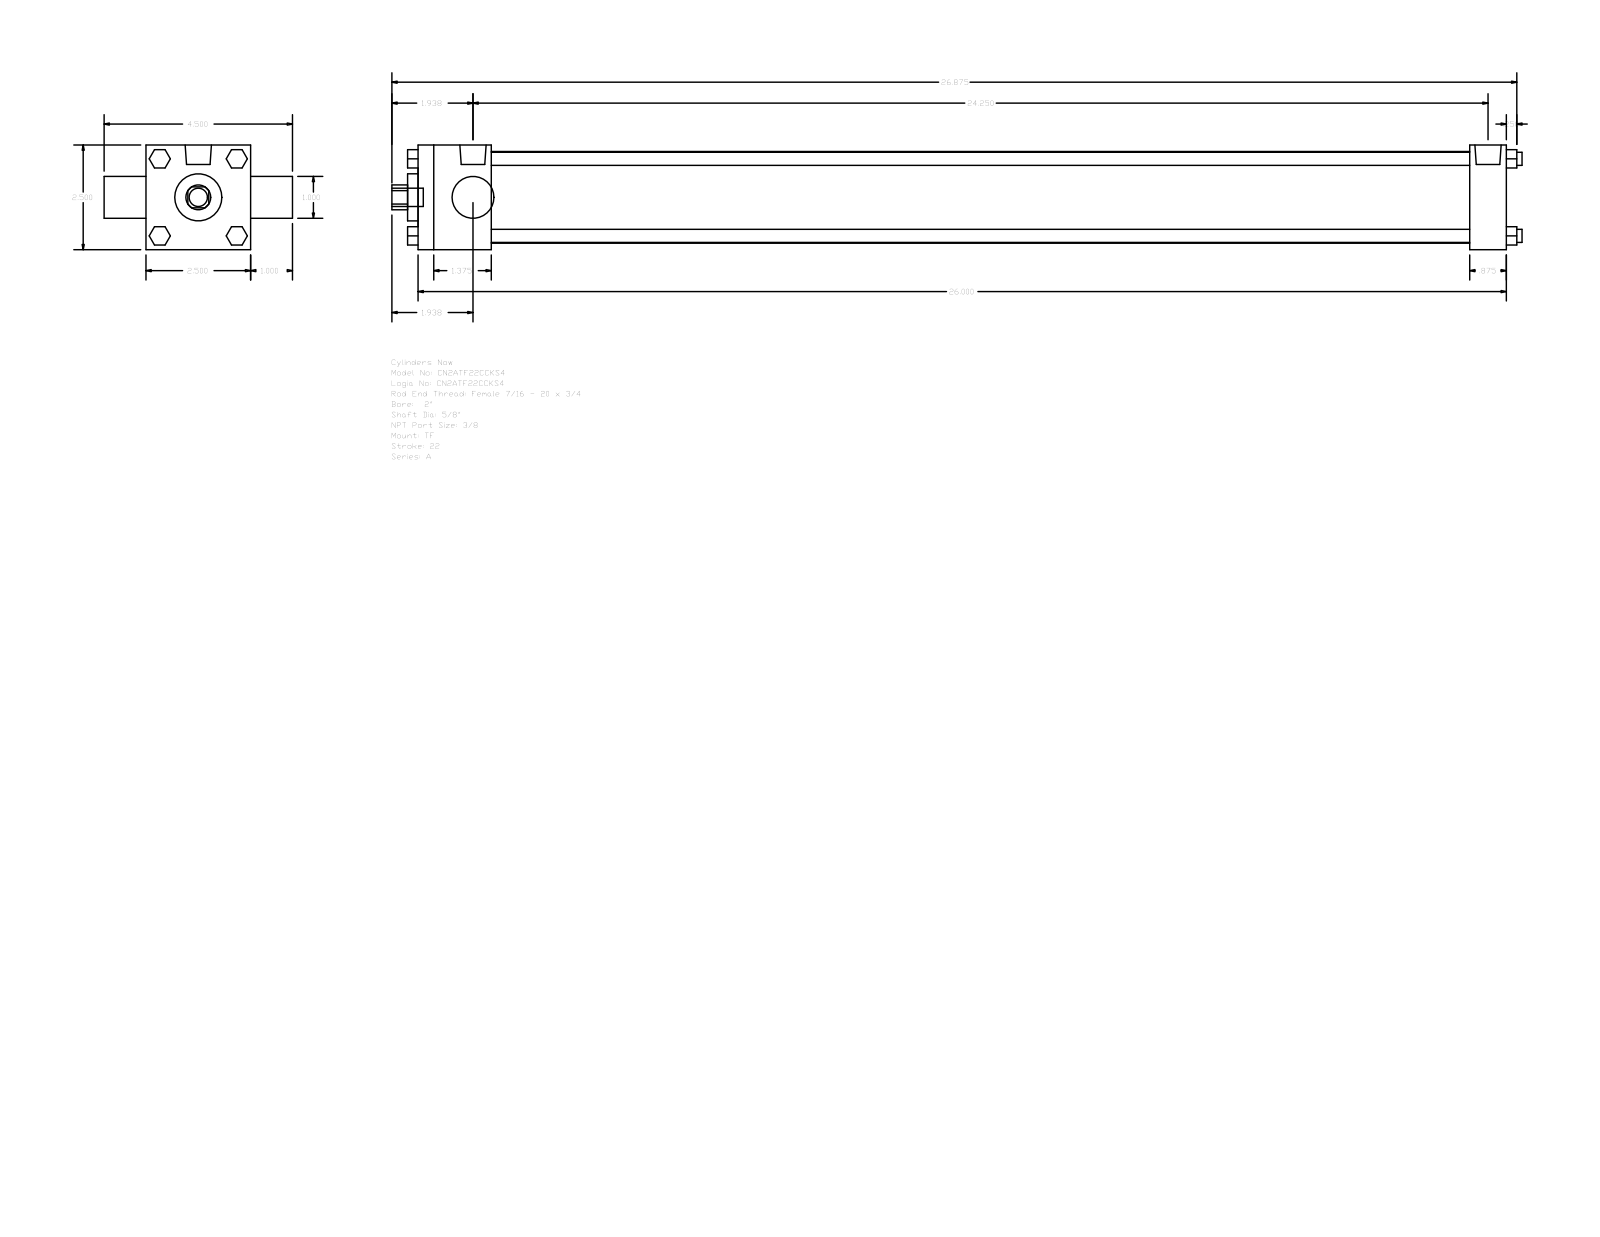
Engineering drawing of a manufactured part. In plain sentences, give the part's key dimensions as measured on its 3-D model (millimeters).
The part is named "A_TF__0200_0.625". Its 3-D file was written by "GSSL Pune (CONFIG_CONTROL_DESIGN)". It is 0 solids with 120 faces: 92 planar, 28 cylindrical and 0 other. Overall it measures 685.8 by 114.3 by 63.5 millimeters. Round holes: 1 of diameter 15.88, 1 of diameter 25.4, 1 of diameter 28.57, 1 of diameter 55.63. Round bosses or shafts: 4 of diameter 7.94, 3 of diameter 5.56, 2 of diameter 15.93, 1 of diameter 11.11. Partial cylindrical surfaces (rounded edges, fillets, slot ends): 1 of radius 7.54. The main face-to-face distances are 63.5, 660.39, 44.45, 638.17, 593.72, 615.94, 22.22, 25.4, 88.9, 6.35.
